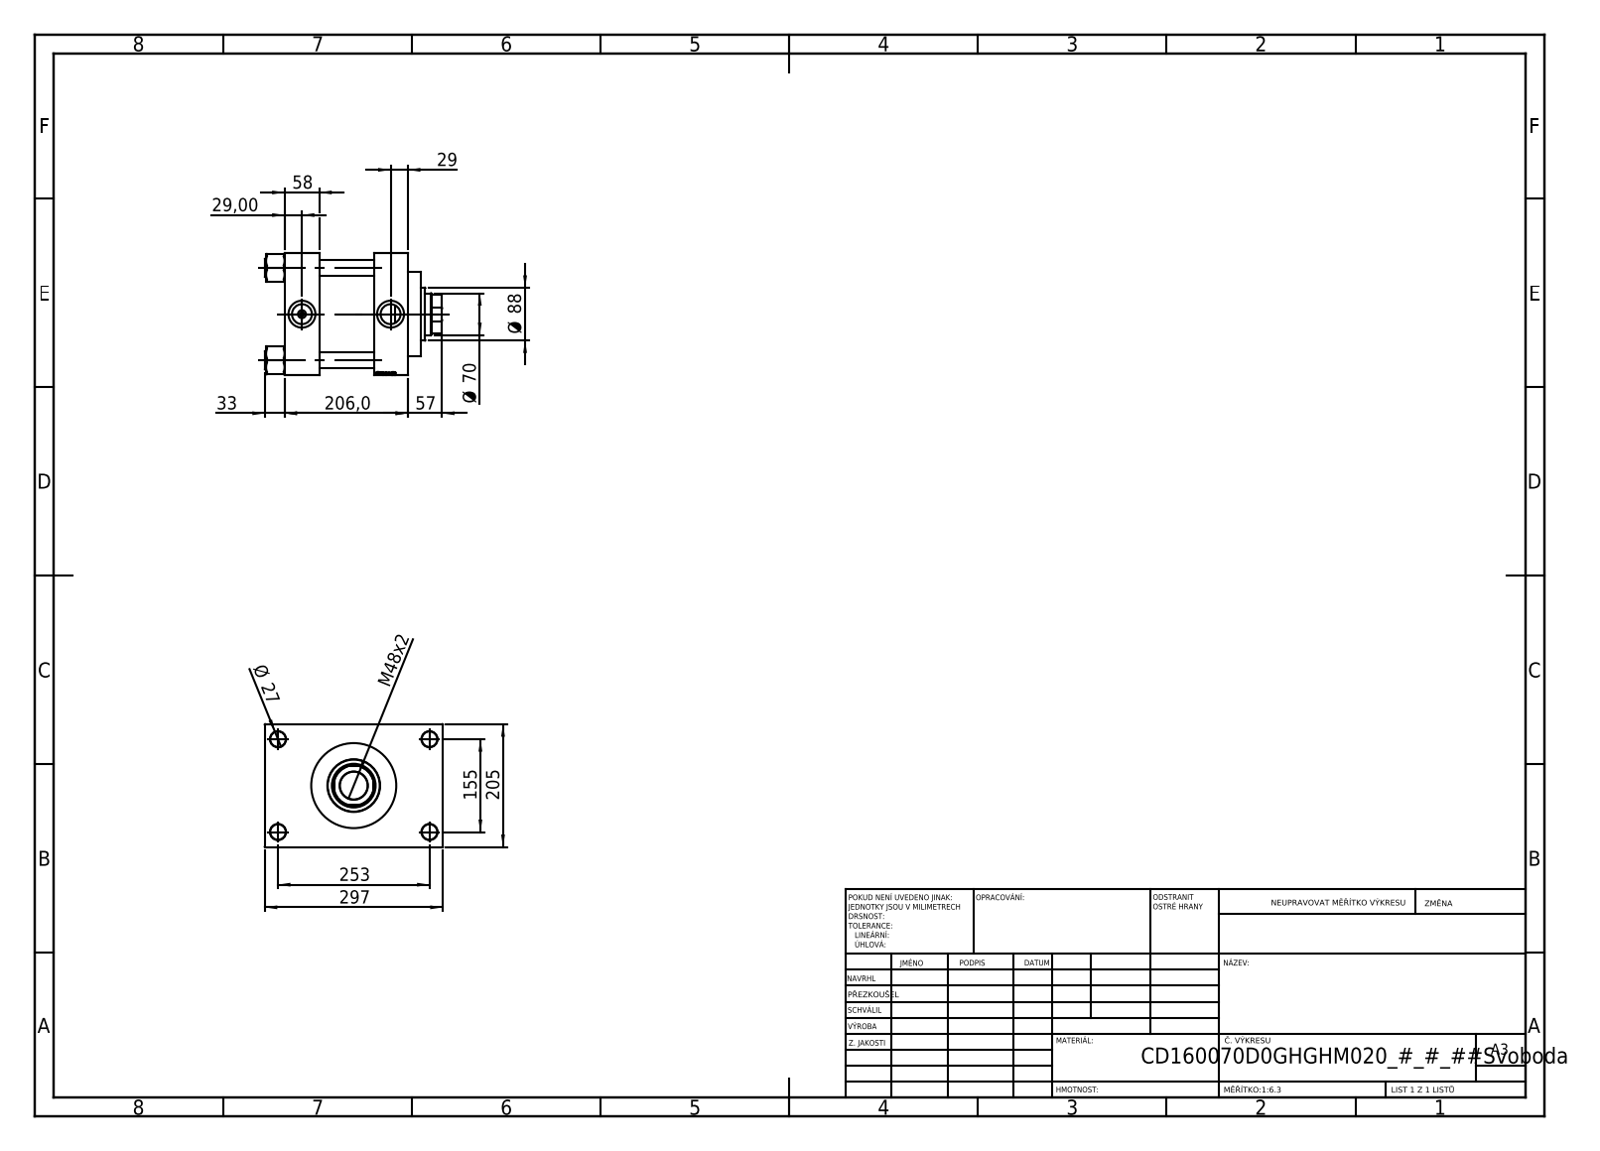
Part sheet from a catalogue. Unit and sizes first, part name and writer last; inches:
Units: inches
Overall size (bounding box): 11.693 × 11.654 × 8.071
Round holes (diameter × count): ⌀1.024 ×4, ⌀1.063 ×4, ⌀0.276 ×2, ⌀1.309 ×2, ⌀1.772 ×2, ⌀1.831 ×1, ⌀2.756 ×1, ⌀2.874 ×1, ⌀4.724 ×1, ⌀5.591 ×1, ⌀6.299 ×1
Round bosses / shafts (diameter × count): ⌀1.181 ×4, ⌀6.535 ×1, ⌀3.465 ×1
Partial cylindrical surfaces — rounded edges, fillets, slot ends (radius × count): R1.339 ×1
Main face-to-face distances: 2.283, 5.906, 3.622, 8.11, 5.827, 2.205, 8.071, 1.811, 9.882, 2.835
Hole centre spacings: 1.931, 4.312, 5.841, 6.098, 6.399, 8.03, 10.084, 6.102
Volume: 479.4 in³ · Surface area: 1 131 in²
Bodies: 11 solids, 1148 faces (544 planar, 86 cylindrical, 518 other)
Part name (STEP PRODUCT): V215CD_NUT_M5_D; V215CD_VCP_D; V215CD_D_TYCINKA; V215CD_D_Body (+1 more)
STEP written by: SolidWorks 2019 (CONFIG_CONTROL_DESIGN)
